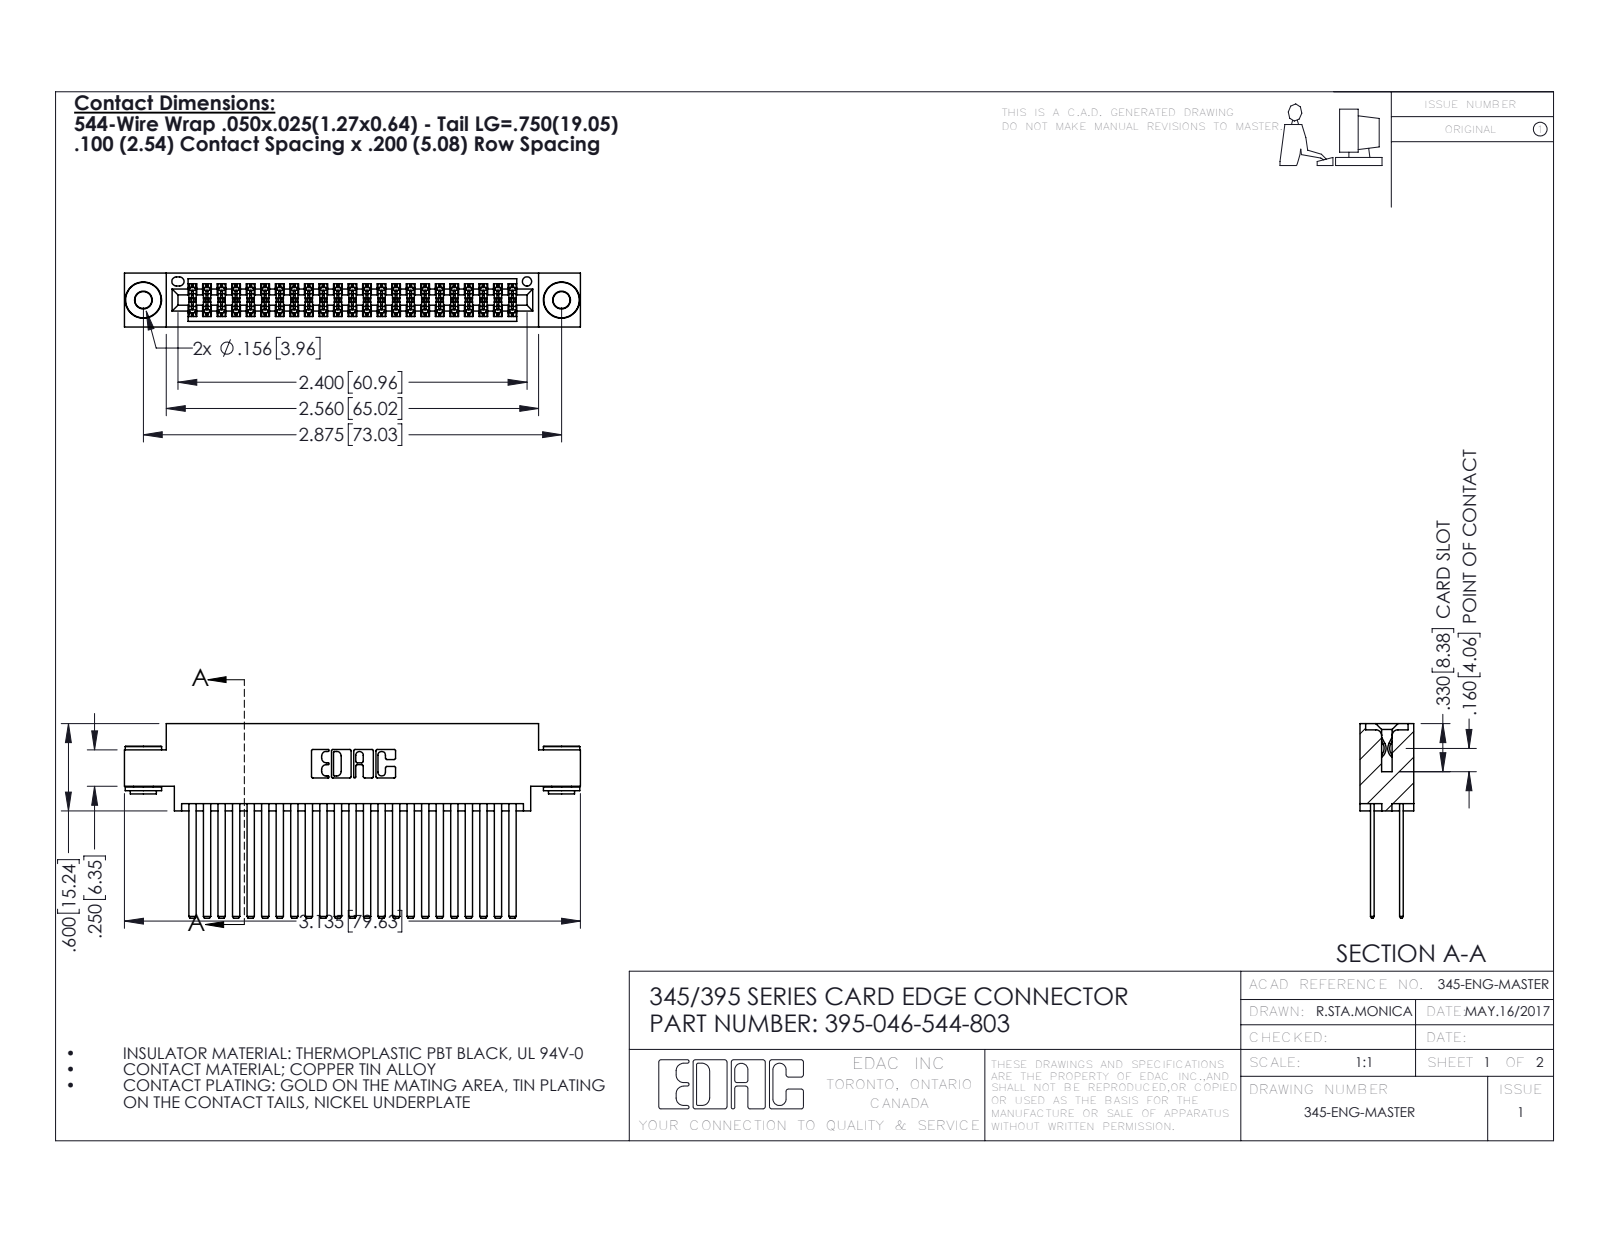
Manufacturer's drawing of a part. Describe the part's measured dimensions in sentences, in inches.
The part is named "345 Part_0.170 Offset - 0.156 Dia-TH; 345-250-002_345-250-002-102; 345-292-001_345-293-144; 395-046-544-803". Its 3-D file was written by "SolidWorks 2016 (CONFIG_CONTROL_DESIGN)". It is 49 solids with 2192 faces: 1428 planar, 756 cylindrical and 8 other. Overall it measures 3.135 by 1.337 by 0.37 inches. Its volume is 0.495 cubic inches and its surface area 21.48 square inches. Round holes: 2 of diameter 0.116, 2 of diameter 0.156, 1 of diameter 0.064. Round bosses or shafts: 2 of diameter 0.25, 2 of diameter 0.18, 2 of diameter 0.136. Partial cylindrical surfaces (rounded edges, fillets, slot ends): 69 of radius 0.006, 22 of radius 0.01, 6 of radius 0.007, 6 of radius 0.031, 3 of radius 0.026, 2 of radius 0.014, 2 of radius 0.019, 2 of radius 0.022. The main face-to-face distances are 0.2, 0.072, 0.298, 0.025, 0.098, 0.272, 0.225, 0.37, 0.175, 0.15. The hole center spacings are 0.27, 2.641, 2.875.
